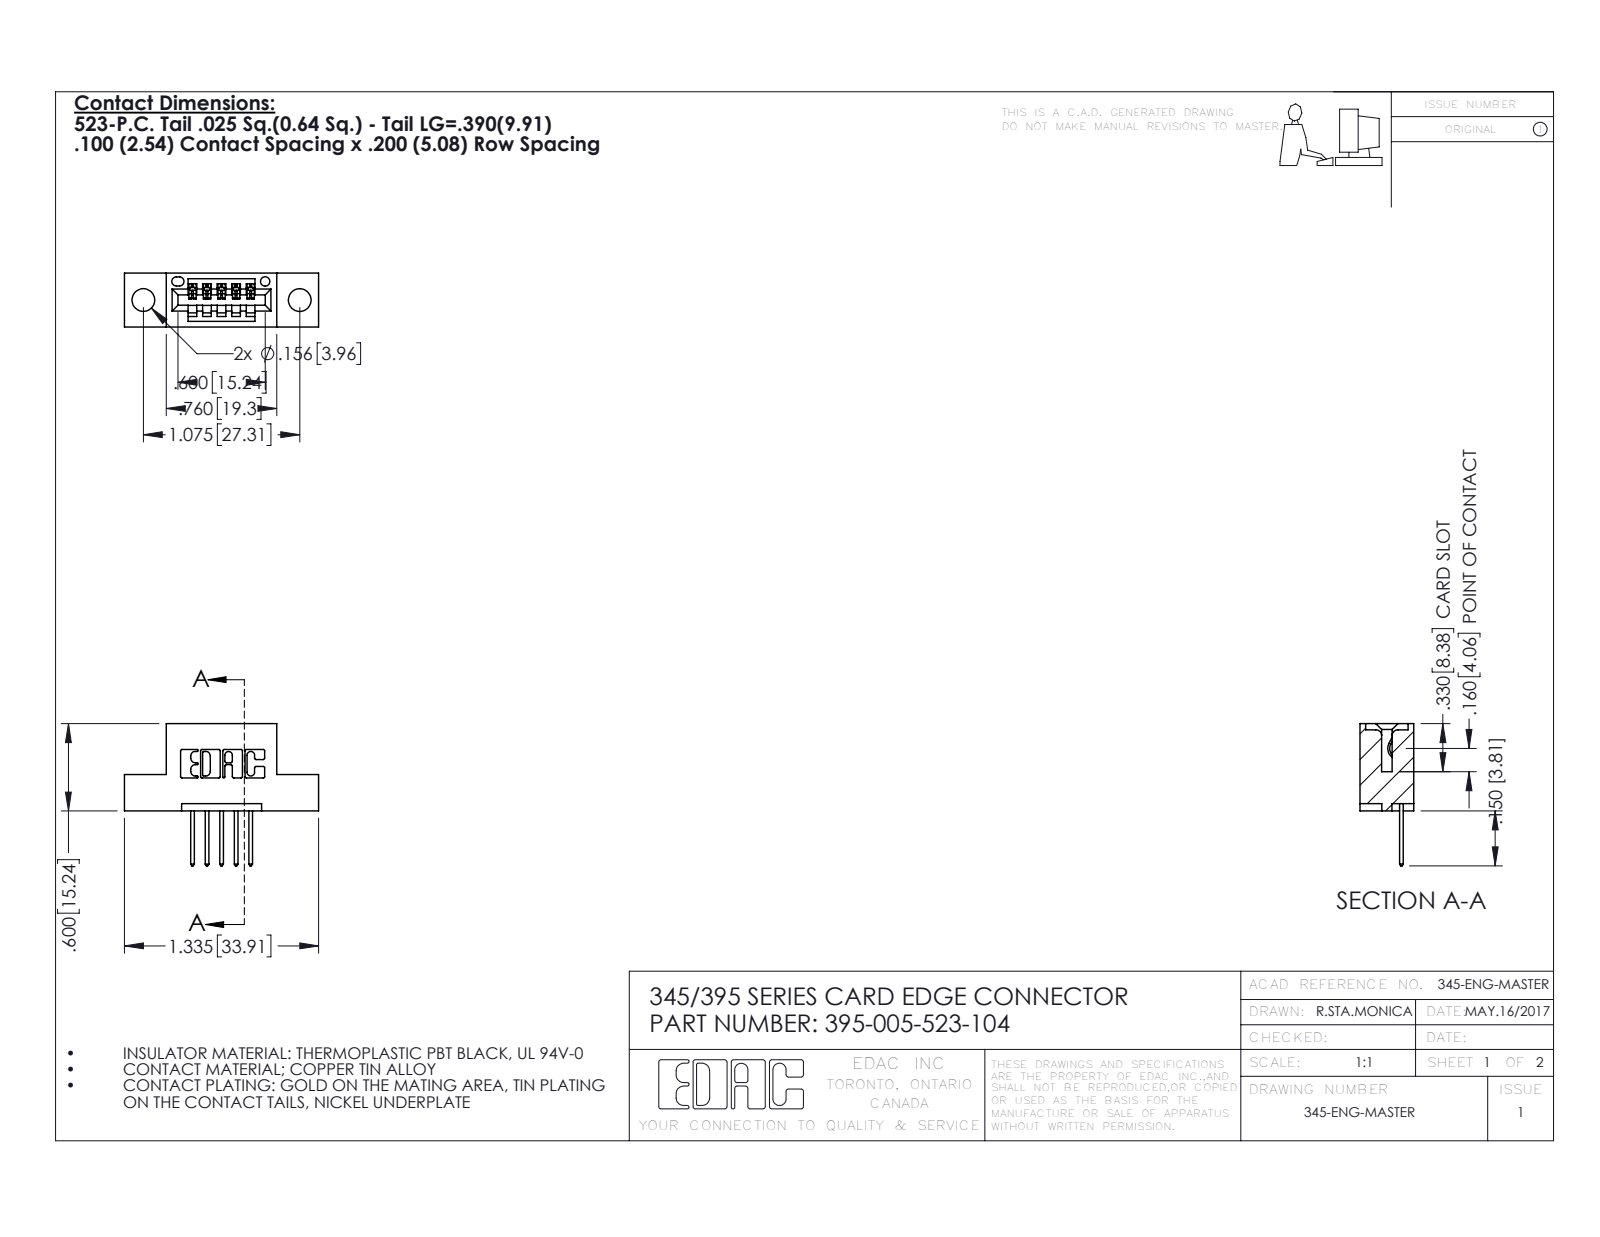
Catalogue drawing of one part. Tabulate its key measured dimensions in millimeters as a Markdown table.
| quantity | value |
| --- | --- |
| part name | 395-005-523-104; 345-292-001_345-293-123; 345 Part_Flush Mounting Lugs - 0.156 Dia-TH |
| STEP written by | SolidWorks 2016 (CONFIG_CONTROL_DESIGN) |
| units | millimeters |
| bodies | 6 solids, 416 faces (280 planar, 136 cylindrical, 0 other) |
| overall size | 33.9 × 24.8 × 9.4 |
| volume | 2 830 mm³ |
| surface area | 3 069 mm² |
| round holes (diameter × count) | 4 × 2, 1.6 × 1 |
| partial cylindrical surfaces (radius × count) | 0.3 × 22, 0.2 × 10, 0.3 × 10, 0.2 × 6, 0.8 × 6, 0.7 × 3, 0.8 × 2, 1 × 2 |
| main face-to-face distances | 5.1, 9.4, 7.6, 1.8, 2.5, 0.6, 6.4, 2.5, 6.9, 1.5 |
| hole center spacings | 6.9, 21.5, 27.3 |
